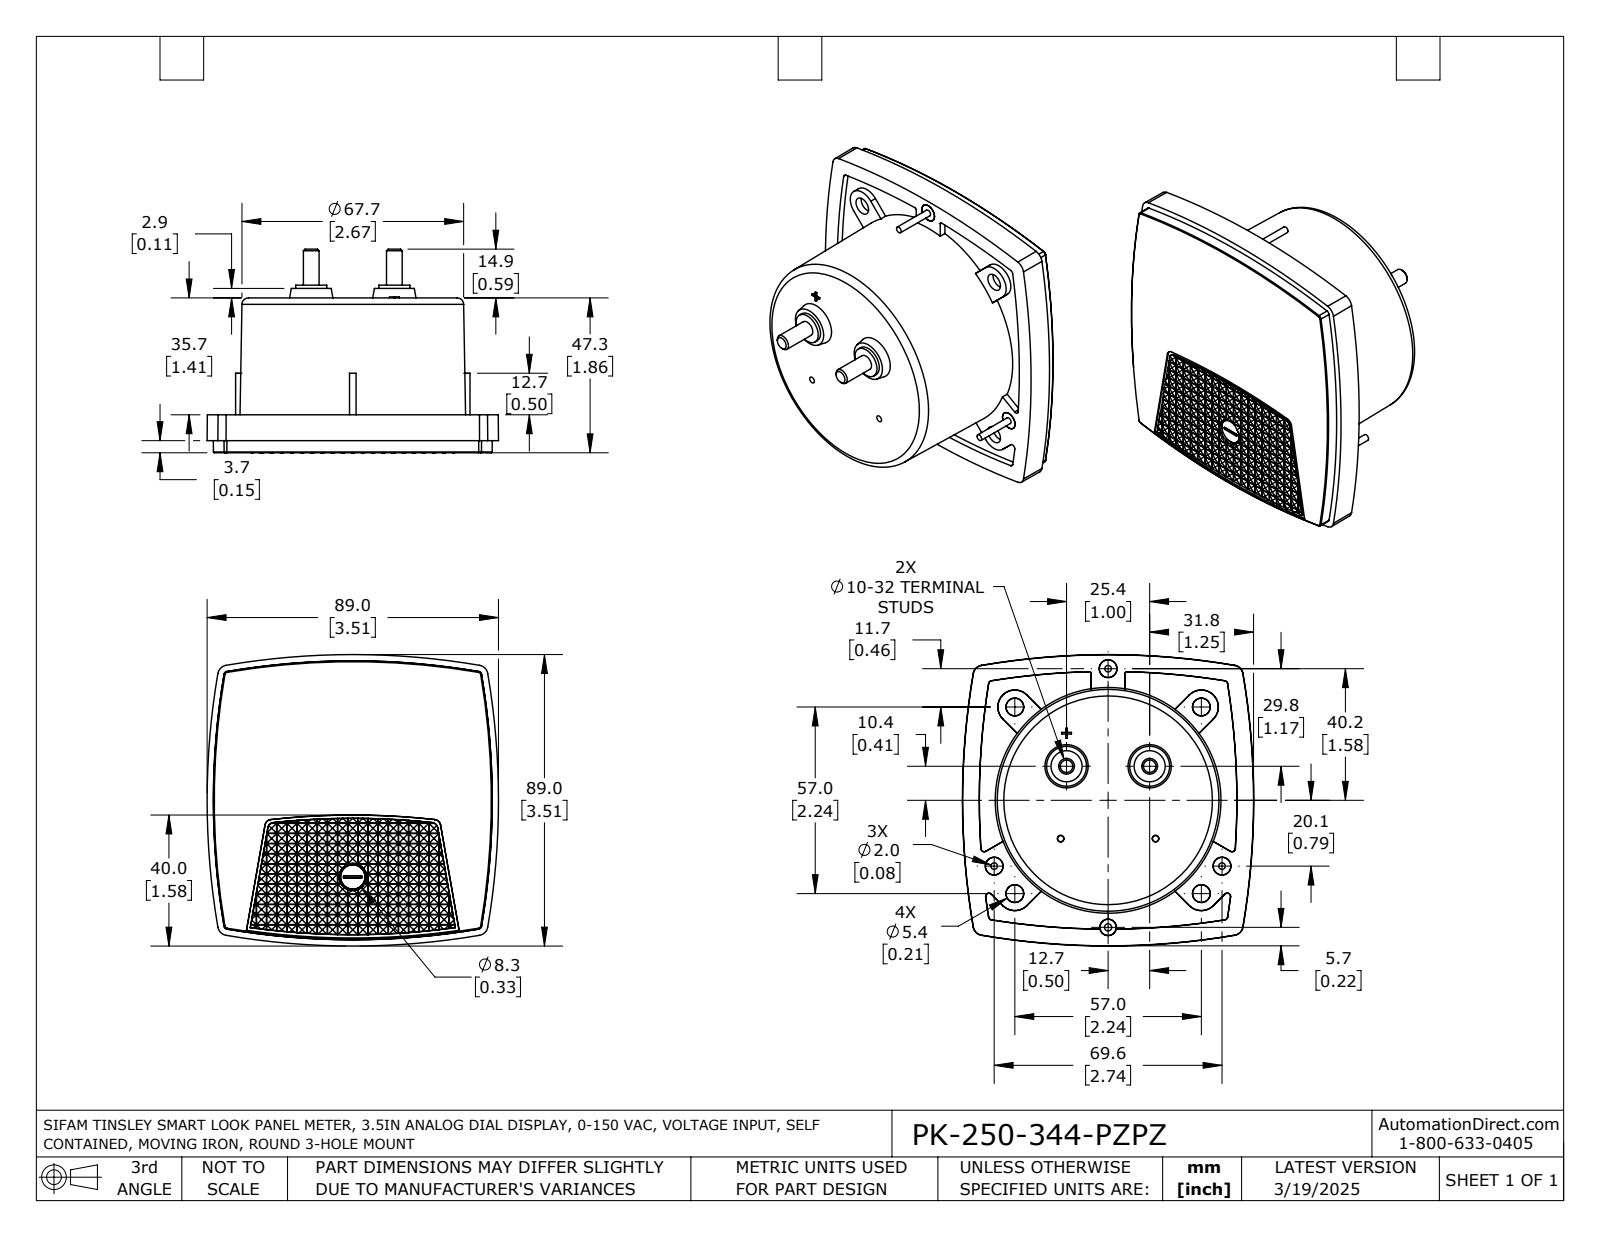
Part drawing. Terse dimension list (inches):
name: PK-250-344-PZPZ
written by: SolidWorks 2021 (AUTOMOTIVE_DESIGN)
unit: in
bodies: 1 solid, 1078 faces (950 planar, 23 cylindrical, 105 other)
size: 3.505 × 3.505 × 2.453
volume: 12.99 in³; area: 44.29 in²
holes: 1× ⌀0.087
bosses: 3× ⌀0.213, 3× ⌀0.079, 2× ⌀0.374, 2× ⌀0.189
rounds: 1× R8.961
face distances: 1.862, 1.406, 0.457, 0.079, 1.484, 0.378, 0.024, 0.096, 0.072, 0.12
